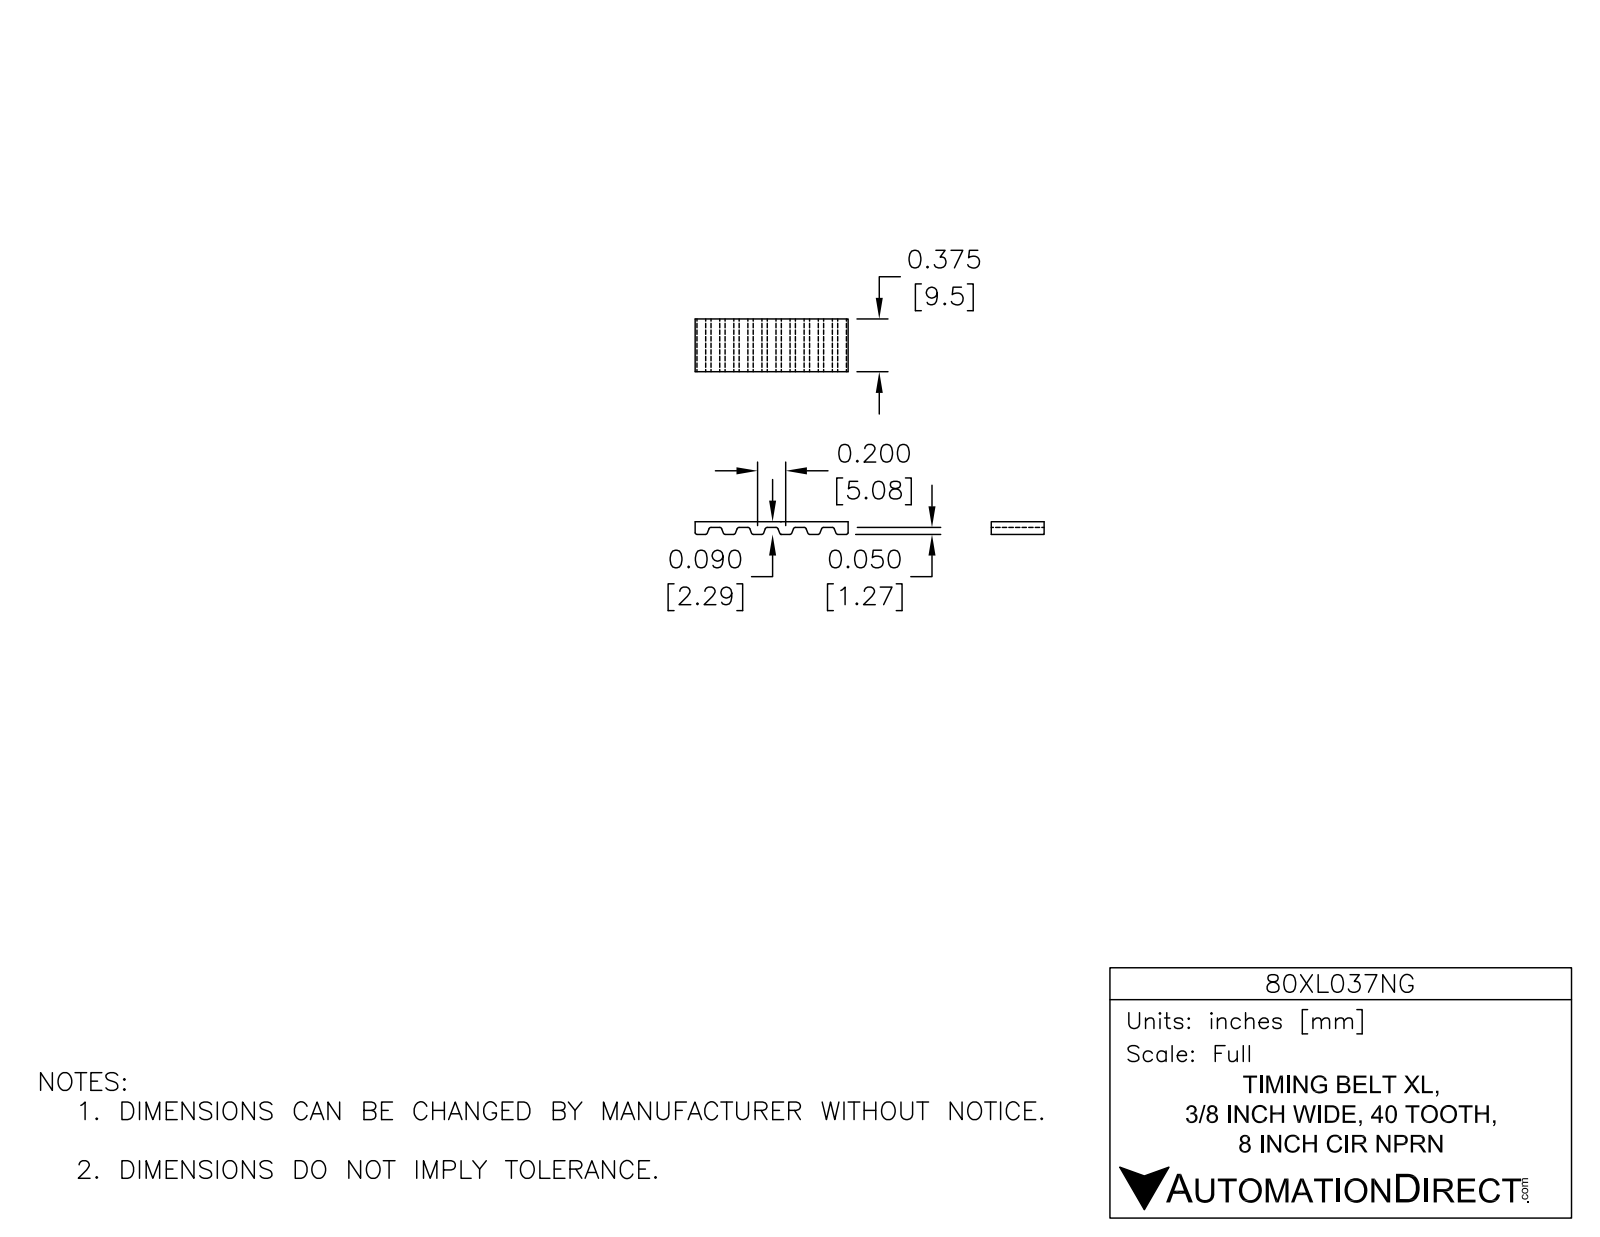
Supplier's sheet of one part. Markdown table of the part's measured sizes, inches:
| quantity | value |
| --- | --- |
| part name | 80XL037NG |
| STEP written by | SolidWorks 2014 (AUTOMOTIVE_DESIGN) |
| units | inches |
| bodies | 1 solid, 349 faces (134 planar, 215 cylindrical, 0 other) |
| overall size | 2.858 × 2 × 0.375 |
| volume | 0.162 in³ |
| surface area | 7.594 in² |
| partial cylindrical surfaces (radius × count) | 0.015 × 160, 0.96 × 2, 1 × 2 |
| main face-to-face distances | 0.375, 2, 0.04, 1.96, 1.92, 0.176, 0.351, 0.09, 1.91, 0.05 |
